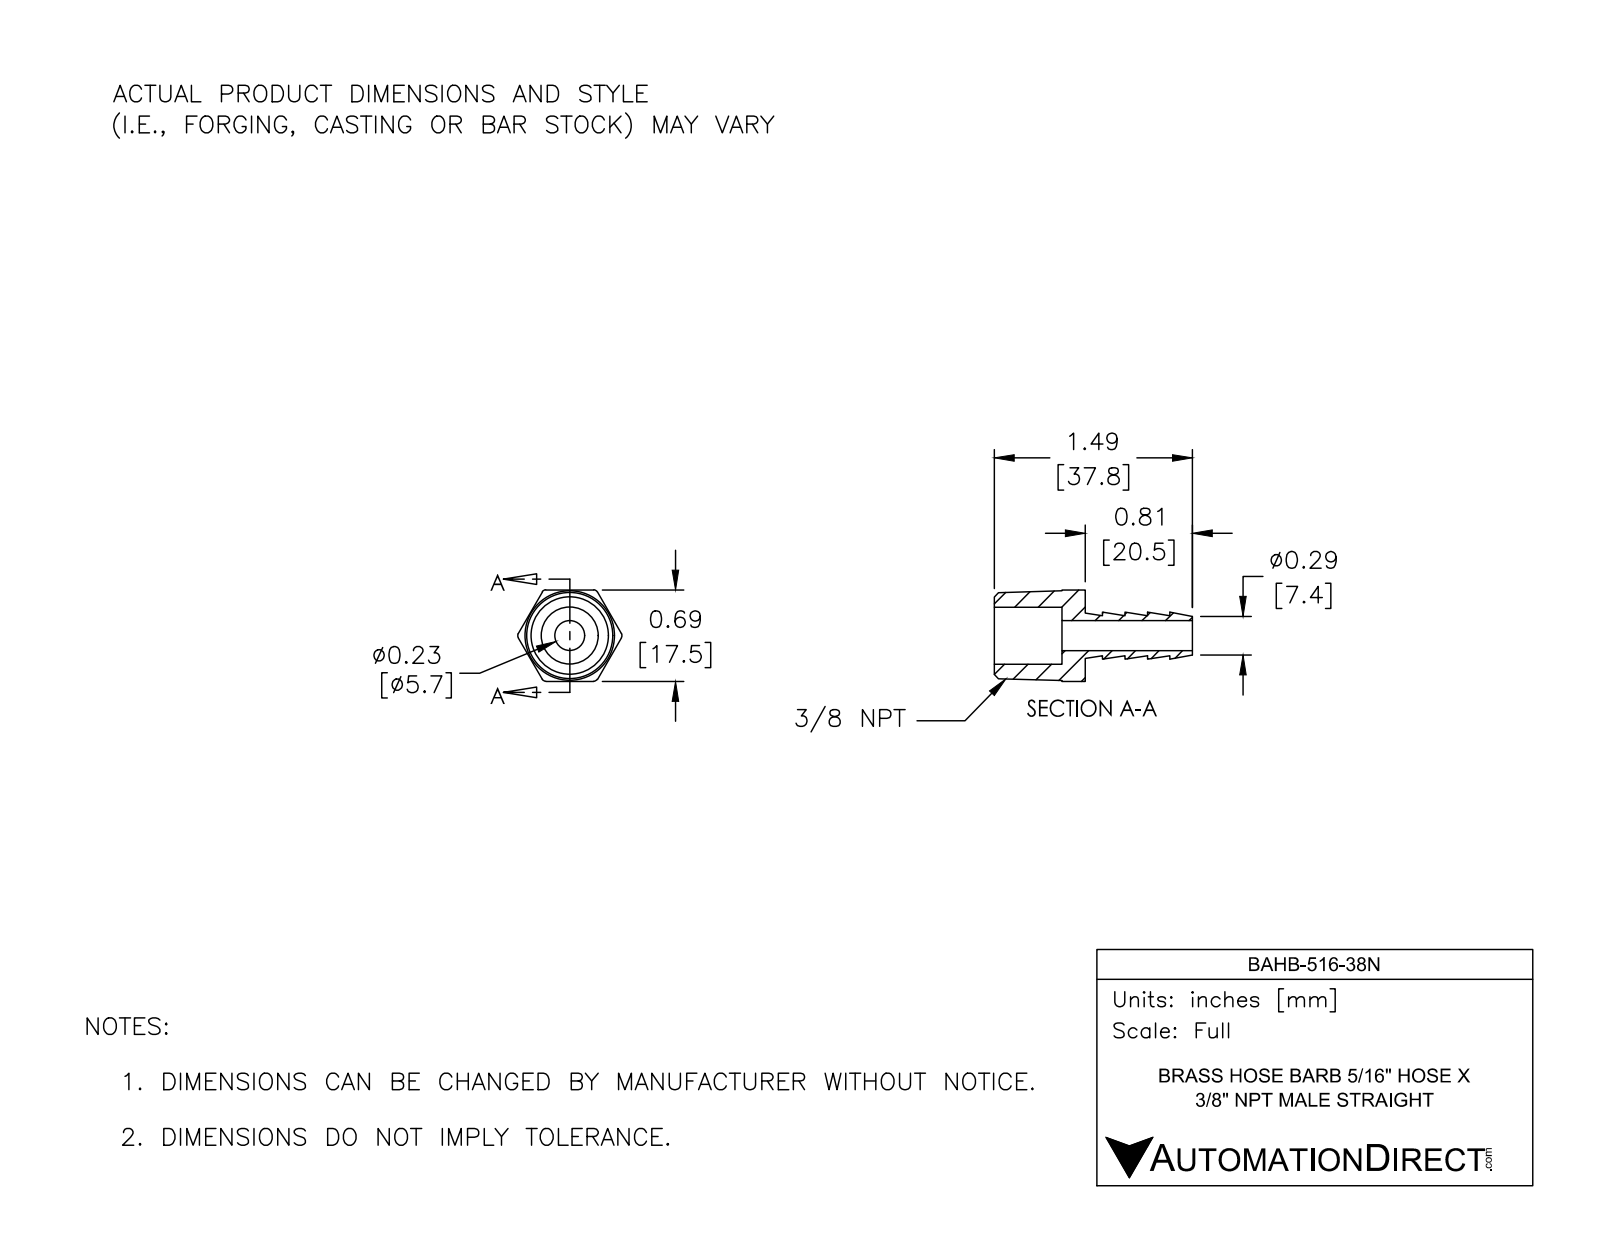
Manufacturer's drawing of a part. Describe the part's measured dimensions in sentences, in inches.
The part is named "BAHB-516-38N". Its 3-D file was written by "SolidWorks 2017 (AUTOMOTIVE_DESIGN)". It is 1 solid with 39 faces: 15 planar, 10 cylindrical and 14 other. Overall it measures 1.49 by 0.785 by 0.687 inches. Its volume is 0.199 cubic inches and its surface area 4.449 square inches. Round holes: 1 of diameter 0.226, 1 of diameter 0.43. Partial cylindrical surfaces (rounded edges, fillets, slot ends): 6 of radius 0.03. The main face-to-face distances are 0.687, 0.176, 0.684, 0.508, 0.169, 0.338, 0.806, 0.982, 1.49, 0.169.
